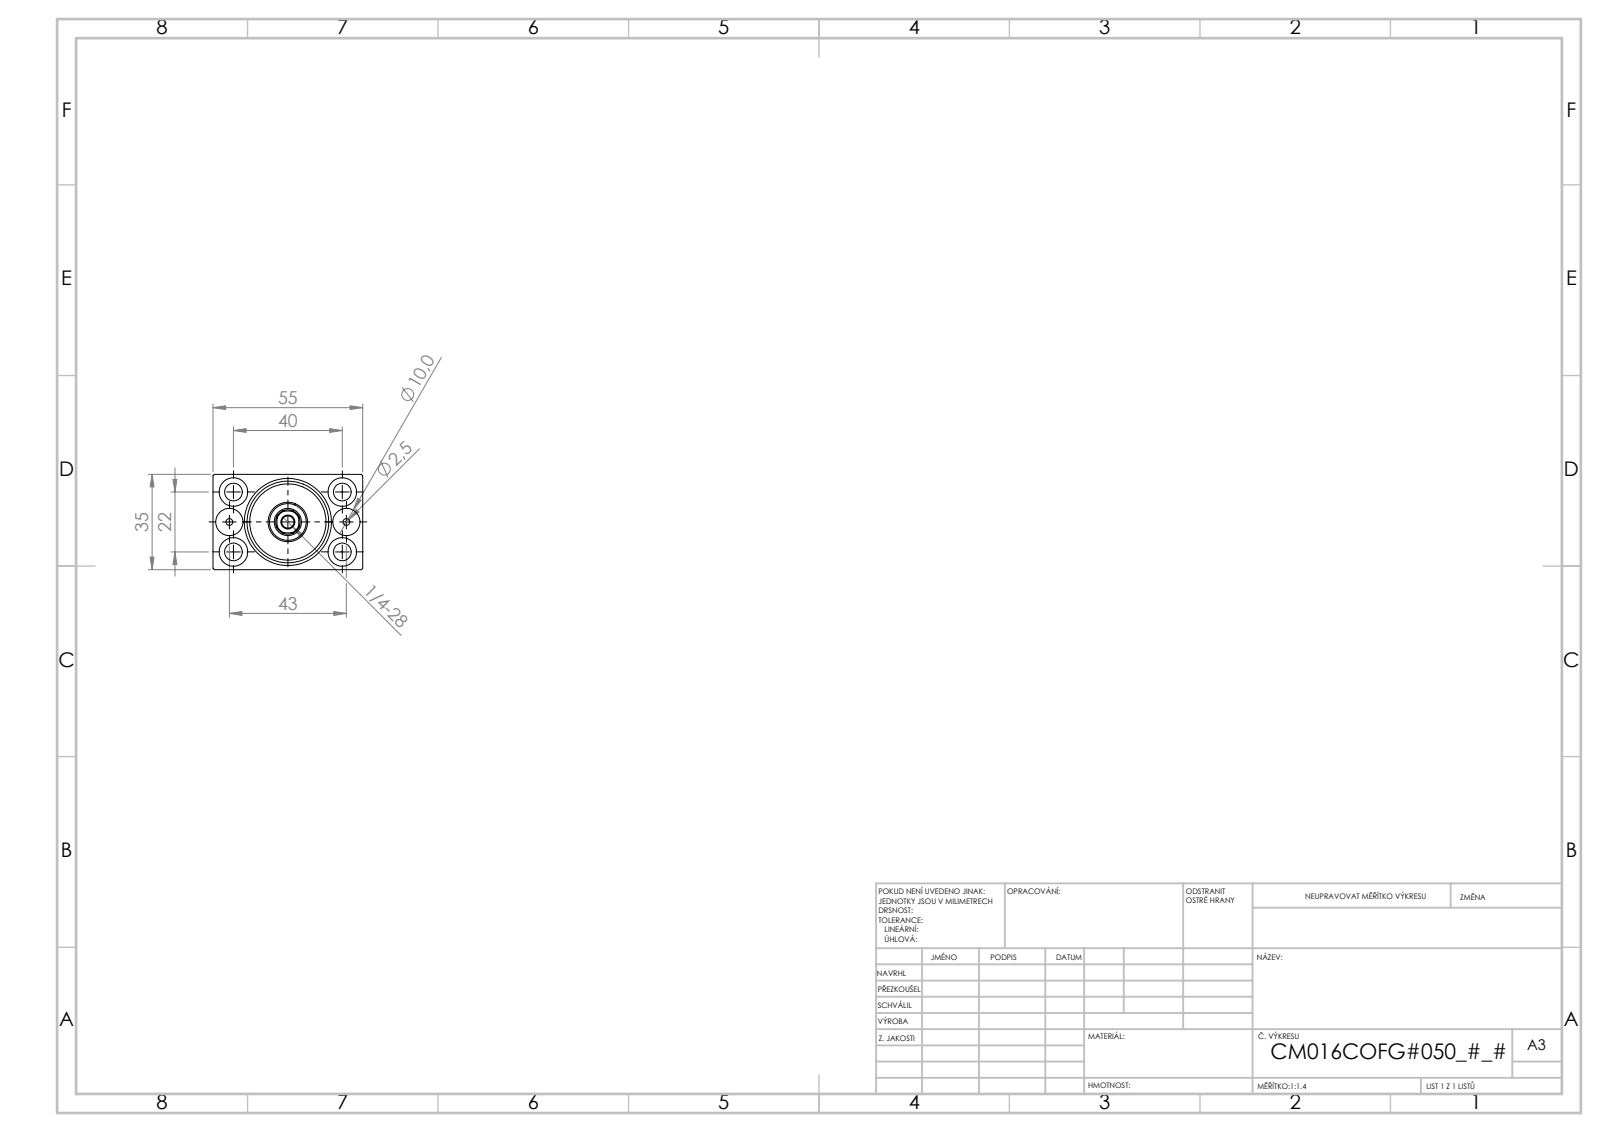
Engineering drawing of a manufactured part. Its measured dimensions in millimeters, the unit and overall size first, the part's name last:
Units: millimetres
Overall size (bounding box): 105 × 55 × 35
Round holes (diameter × count): ⌀6.5 ×4, ⌀10.5 ×4, ⌀10 ×3, ⌀2.5 ×2, ⌀4.5 ×1, ⌀13.5 ×1, ⌀14.5 ×1, ⌀16 ×1, ⌀18 ×1, ⌀30 ×1
Partial cylindrical surfaces — rounded edges, fillets, slot ends (radius × count): R4.5 ×1
Main face-to-face distances: 35, 55, 91, 5, 2, 96, 3, 86, 8, 99
Hole centre spacings: 11.1, 22.83, 42.93, 21.5, 22, 40, 45.65, 43
Volume: 162 625 mm³ · Surface area: 42 964 mm²
Bodies: 3 solids, 861 faces (409 planar, 58 cylindrical, 394 other)
Part name (STEP PRODUCT): V450CM_C_VCP; V450CM_VC_B; V450CM_C_Body
STEP written by: SolidWorks 2019 (CONFIG_CONTROL_DESIGN)
